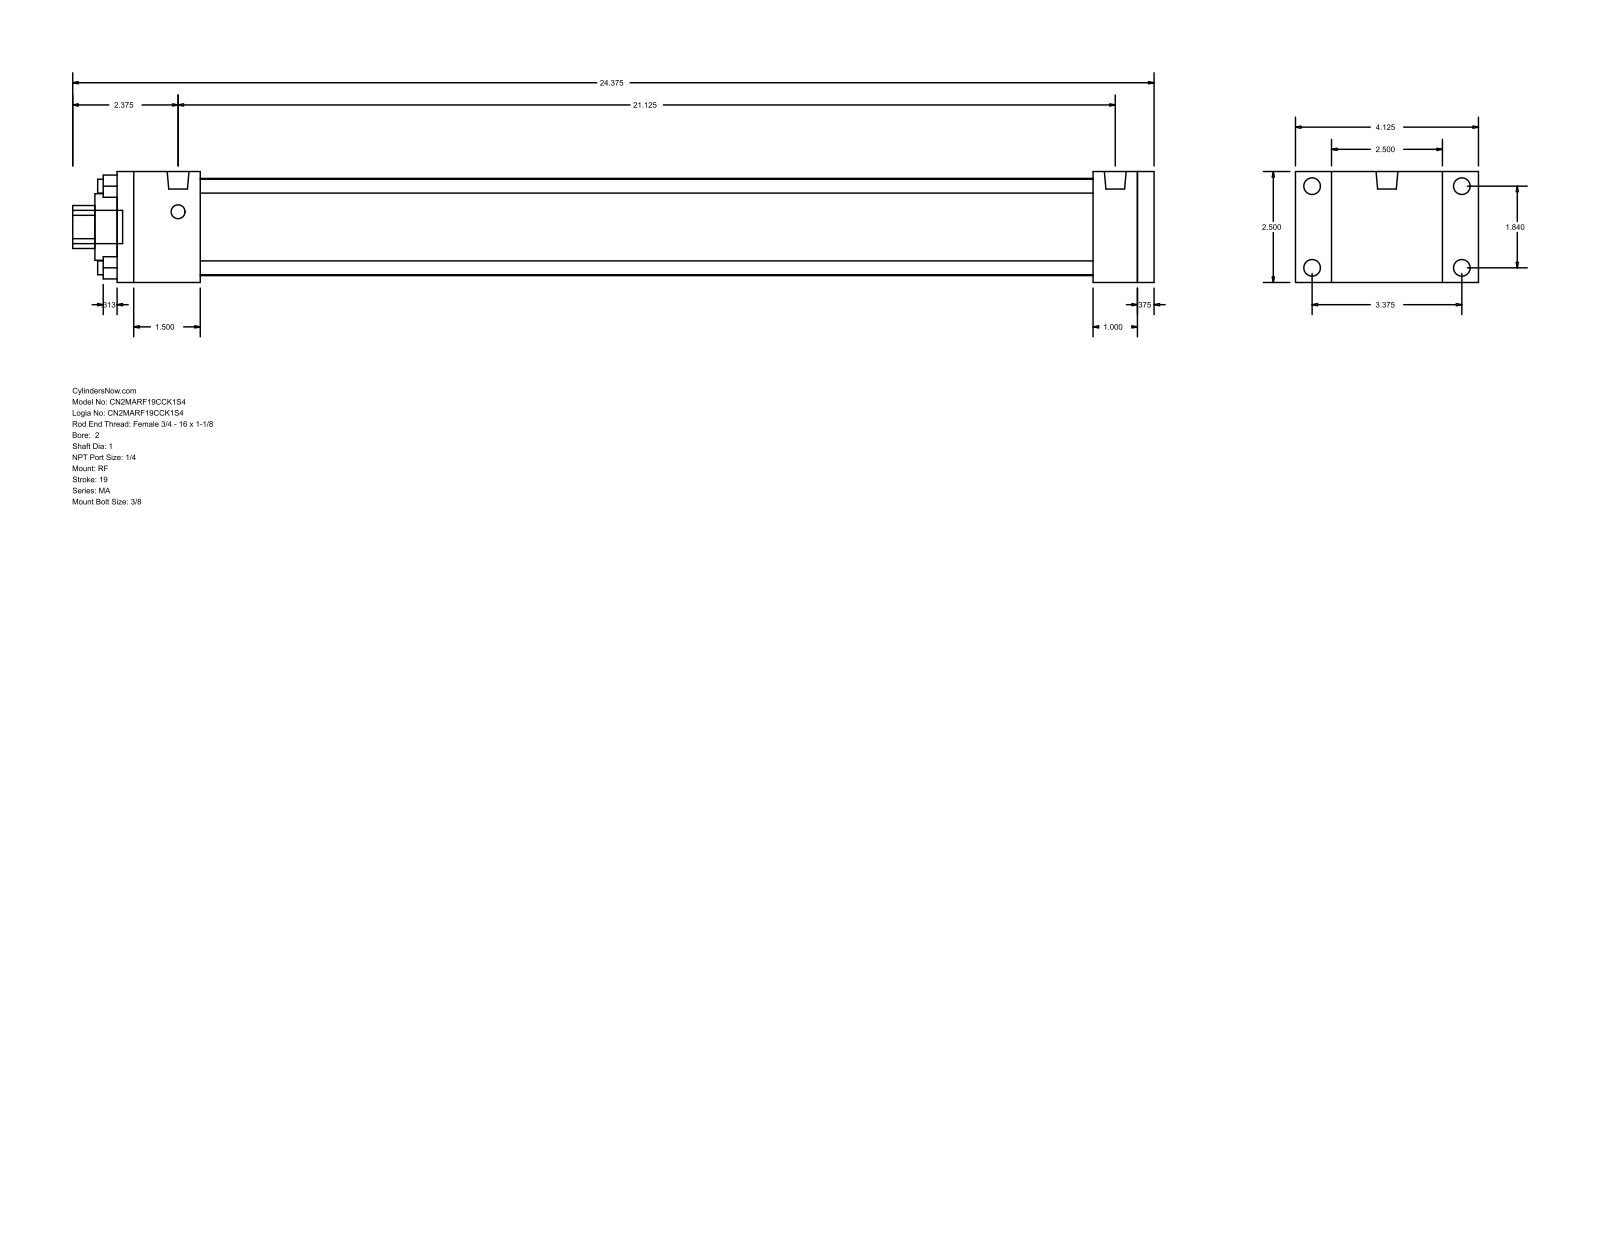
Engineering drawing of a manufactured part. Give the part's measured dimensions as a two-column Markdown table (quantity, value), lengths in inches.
| quantity | value |
| --- | --- |
| part name | MA_RF__0200_1 |
| STEP written by | GSSL Pune (CONFIG_CONTROL_DESIGN) |
| units | inches |
| bodies | 0 solids, 92 faces (64 planar, 28 cylindrical, 0 other) |
| overall size | 24.375 × 4.125 × 2.5 |
| round holes (diameter × count) | 0.313 × 4, 1 × 1, 1.5 × 1, 2.19 × 1 |
| round bosses / shafts (diameter × count) | 0.375 × 4, 0.313 × 4, 0.492 × 2, 0.75 × 1 |
| partial cylindrical surfaces (radius × count) | 0.484 × 1 |
| main face-to-face distances | 2.5, 23, 0.375, 23.375, 1, 0.813, 0.5, 1.875, 21.125, 21.5 |
| hole center spacings | 1.301, 1.84, 2.602 |
